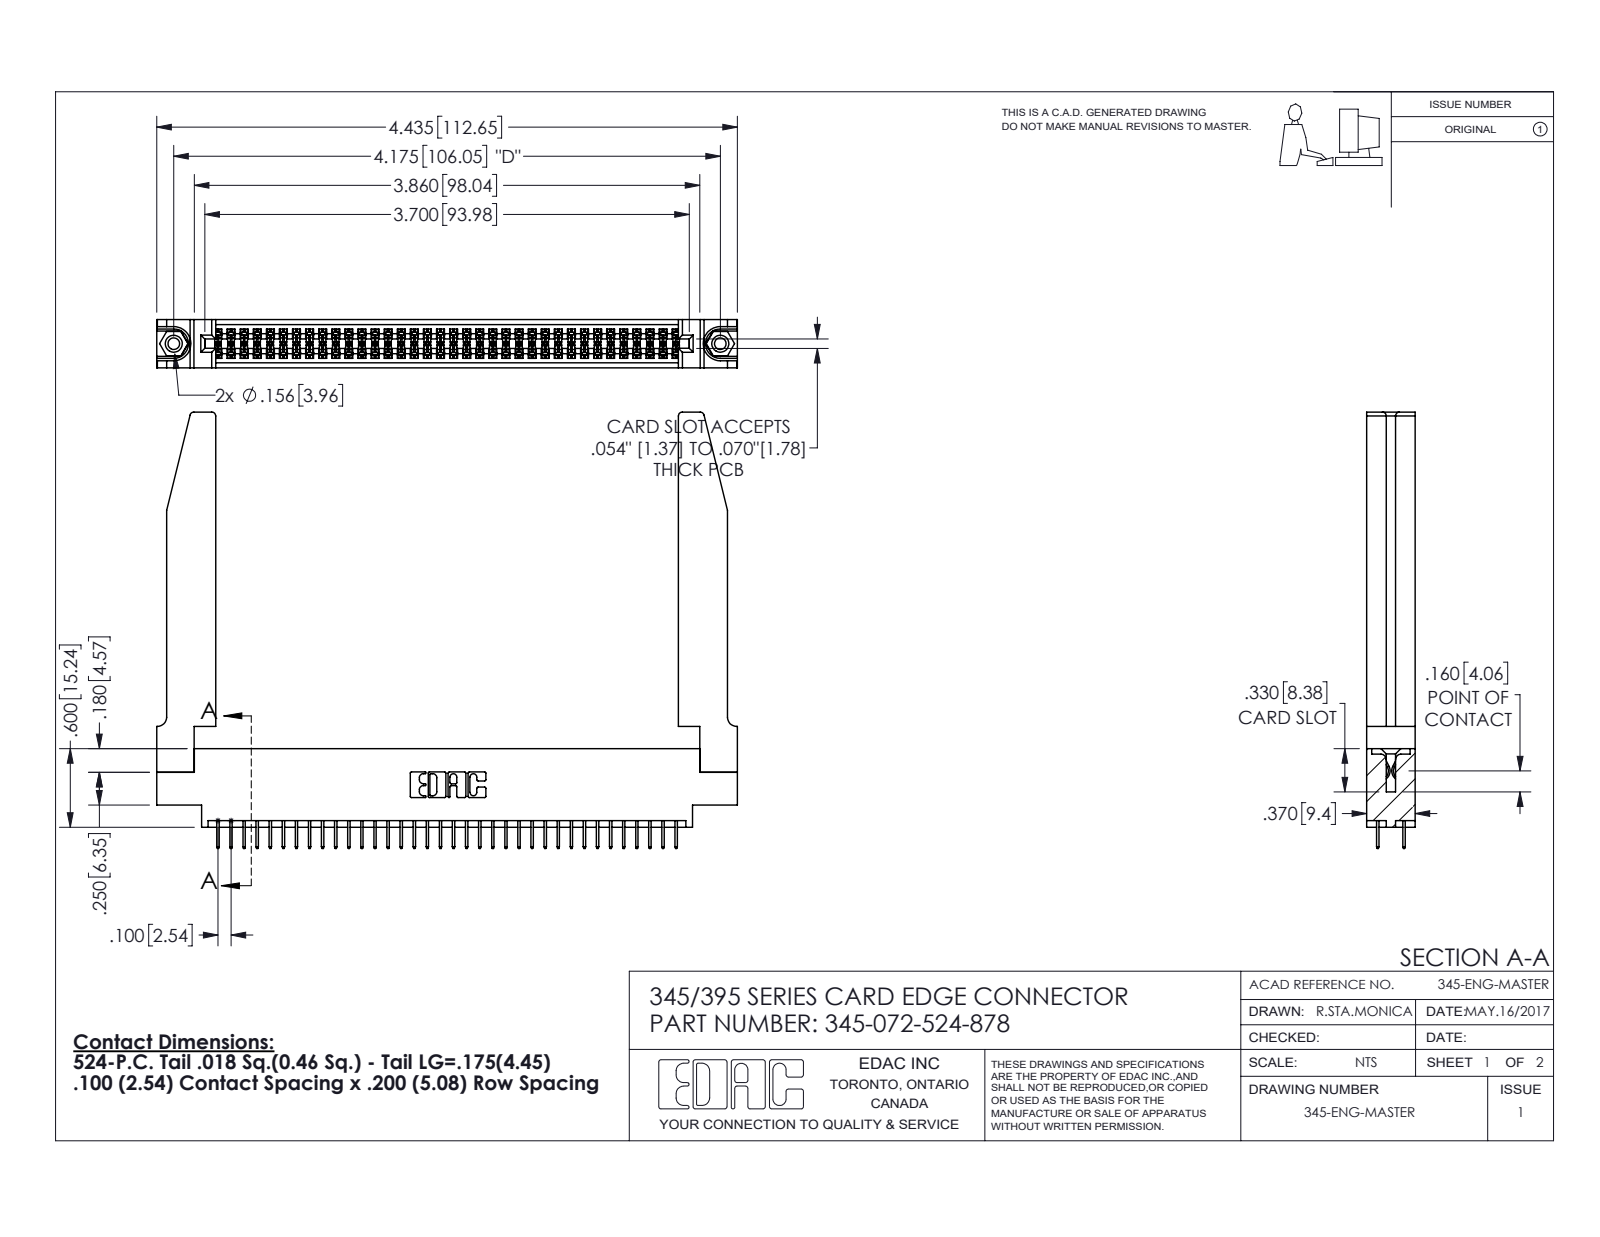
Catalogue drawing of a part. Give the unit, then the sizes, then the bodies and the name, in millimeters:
Units: millimetres
Overall size (bounding box): 112.7 × 84.6 × 9.4
Round holes (diameter × count): ⌀2.3 ×2, ⌀3.2 ×2, ⌀4 ×2, ⌀1.6 ×1
Round bosses / shafts (diameter × count): ⌀3.9 ×2
Partial cylindrical surfaces — rounded edges, fillets, slot ends (radius × count): R0.2 ×108, R0.3 ×22, R0.8 ×8, R0.2 ×6, R0.8 ×6, R0.7 ×3, R0.4 ×2, R0.5 ×2
Main face-to-face distances: 9.4, 1.8, 7.6, 5.1, 2.5, 6.9, 0.6, 5.7, 3.8, 3.8
Hole centre spacings: 6.9, 100.1, 106
Volume: 18 440 mm³ · Surface area: 22 350 mm²
Bodies: 77 solids, 4252 faces (3034 planar, 1166 cylindrical, 52 other)
Part name (STEP PRODUCT): 345-292-001_345-293-124; 345-250-001_345-250-001-102; 345 Part_0.170 Offset - 0.156 Dia-TH; 345-072-524-878 (+1 more)
STEP written by: SolidWorks 2016 (CONFIG_CONTROL_DESIGN)
